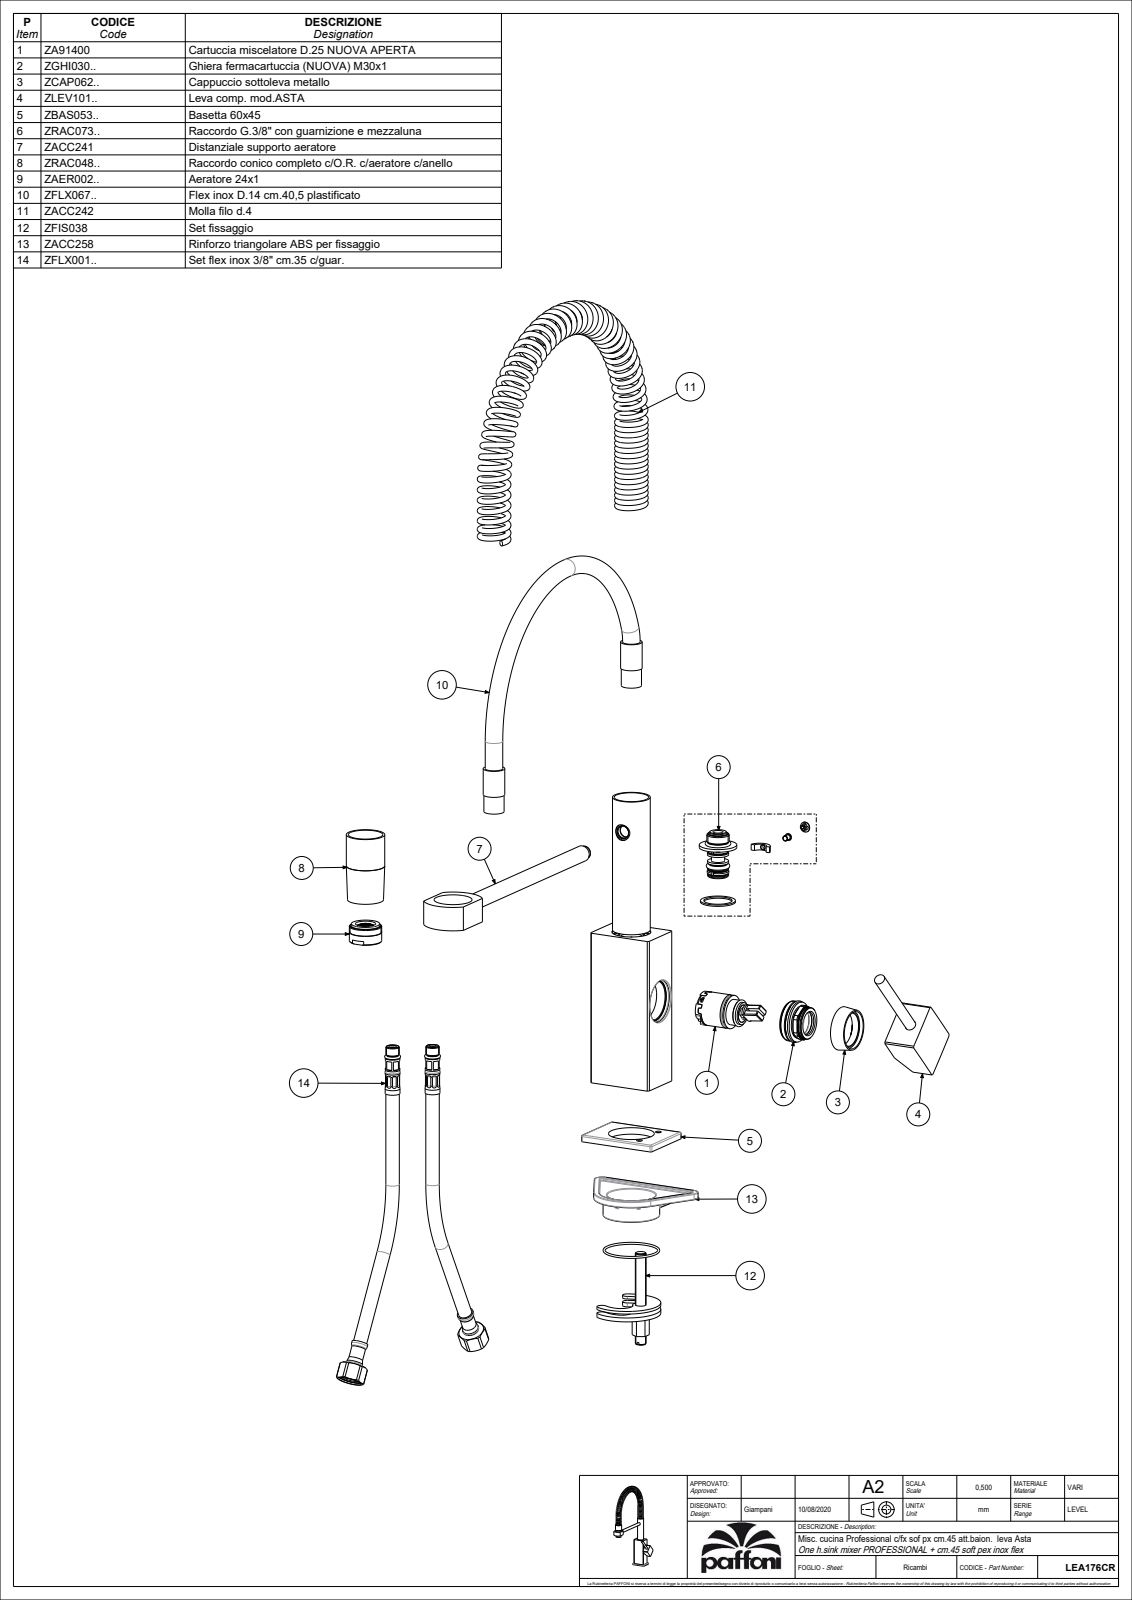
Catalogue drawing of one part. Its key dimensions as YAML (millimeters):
part_name: "LEA176CR"
step_written_by: "CREO PARAMETRIC BY PTC INC, 2020044 (CONFIG_CONTROL_DESIGN)"
units: millimeters
bodies: {solids: 5, faces: 2380, planar: 1647, cylindrical: 366, other: 367}
overall_size: [395.74, 251.82, 82.98]
volume: 416730
surface_area: 161761
round_holes:
  - {diameter: 11, count: 3}
  - {diameter: 5, count: 2}
  - {diameter: 6, count: 2}
  - {diameter: 9, count: 2}
  - {diameter: 14, count: 2}
  - {diameter: 16, count: 2}
  - {diameter: 25.5, count: 2}
  - {diameter: 34, count: 2}
  - {diameter: 3, count: 1}
  - {diameter: 4, count: 1}
  - {diameter: 4.2, count: 1}
  - {diameter: 5.5, count: 1}
round_bosses_or_shafts:
  - {diameter: 20, count: 2}
  - {diameter: 38.8, count: 1}
  - {diameter: 31.5, count: 1}
  - {diameter: 28.5, count: 1}
  - {diameter: 28, count: 1}
  - {diameter: 25, count: 1}
  - {diameter: 24, count: 1}
  - {diameter: 23.8, count: 1}
partial_cylinders:
  - {radius: 0.5, count: 62}
  - {radius: 1, count: 18}
  - {radius: 0.7, count: 10}
  - {radius: 0.8, count: 6}
  - {radius: 0.6, count: 4}
  - {radius: 0.65, count: 4}
  - {radius: 0.85, count: 4}
  - {radius: 2, count: 4}
face_to_face_distances: [36, 50, 8, 1, 5, 120, 18, 42, 3, 7]
hole_center_spacings: [5.96, 6.72, 9.43, 11.31, 15.26, 1.16, 3, 5]
